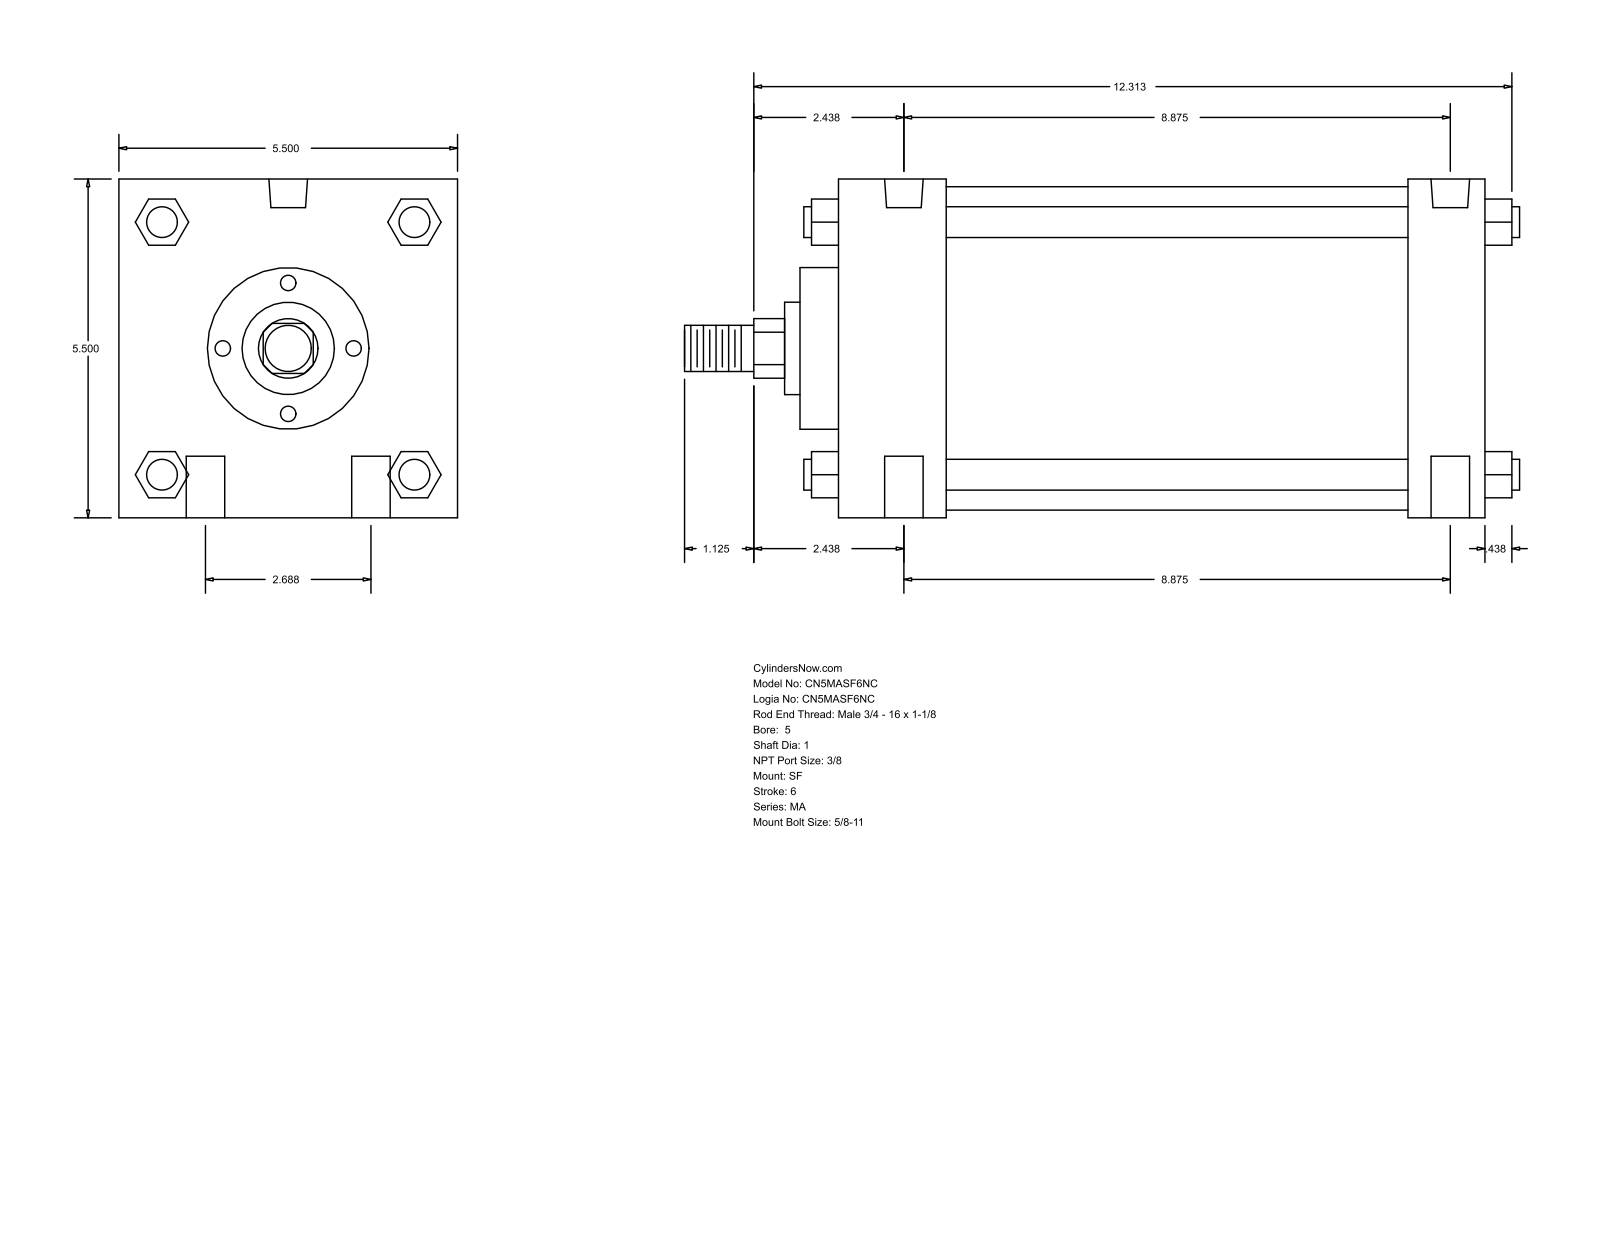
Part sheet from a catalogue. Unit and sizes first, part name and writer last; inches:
Units: inches
Overall size (bounding box): 13.563 × 5.5 × 5.5
Round holes (diameter × count): ⌀0.625 ×4, ⌀0.437 ×2, ⌀0.627 ×2
Round bosses / shafts (diameter × count): ⌀0.5 ×4, ⌀5.25 ×1, ⌀2.625 ×1, ⌀1.5 ×1, ⌀1 ×1, ⌀0.75 ×1
Partial cylindrical surfaces — rounded edges, fillets, slot ends (radius × count): R0.484 ×1
Main face-to-face distances: 5.5, 10.5, 1.75, 9.25, 7.5, 8.75, 1.25, 0.625, 2.375, 9.875
Hole centre spacings: 1.344, 8.976, 8.875, 2.687, 9.273, 8.5
Bodies: 0 solids, 126 faces (95 planar, 31 cylindrical, 0 other)
Part name (STEP PRODUCT): MA_SF__0500_1
STEP written by: GSSL Pune (CONFIG_CONTROL_DESIGN)
